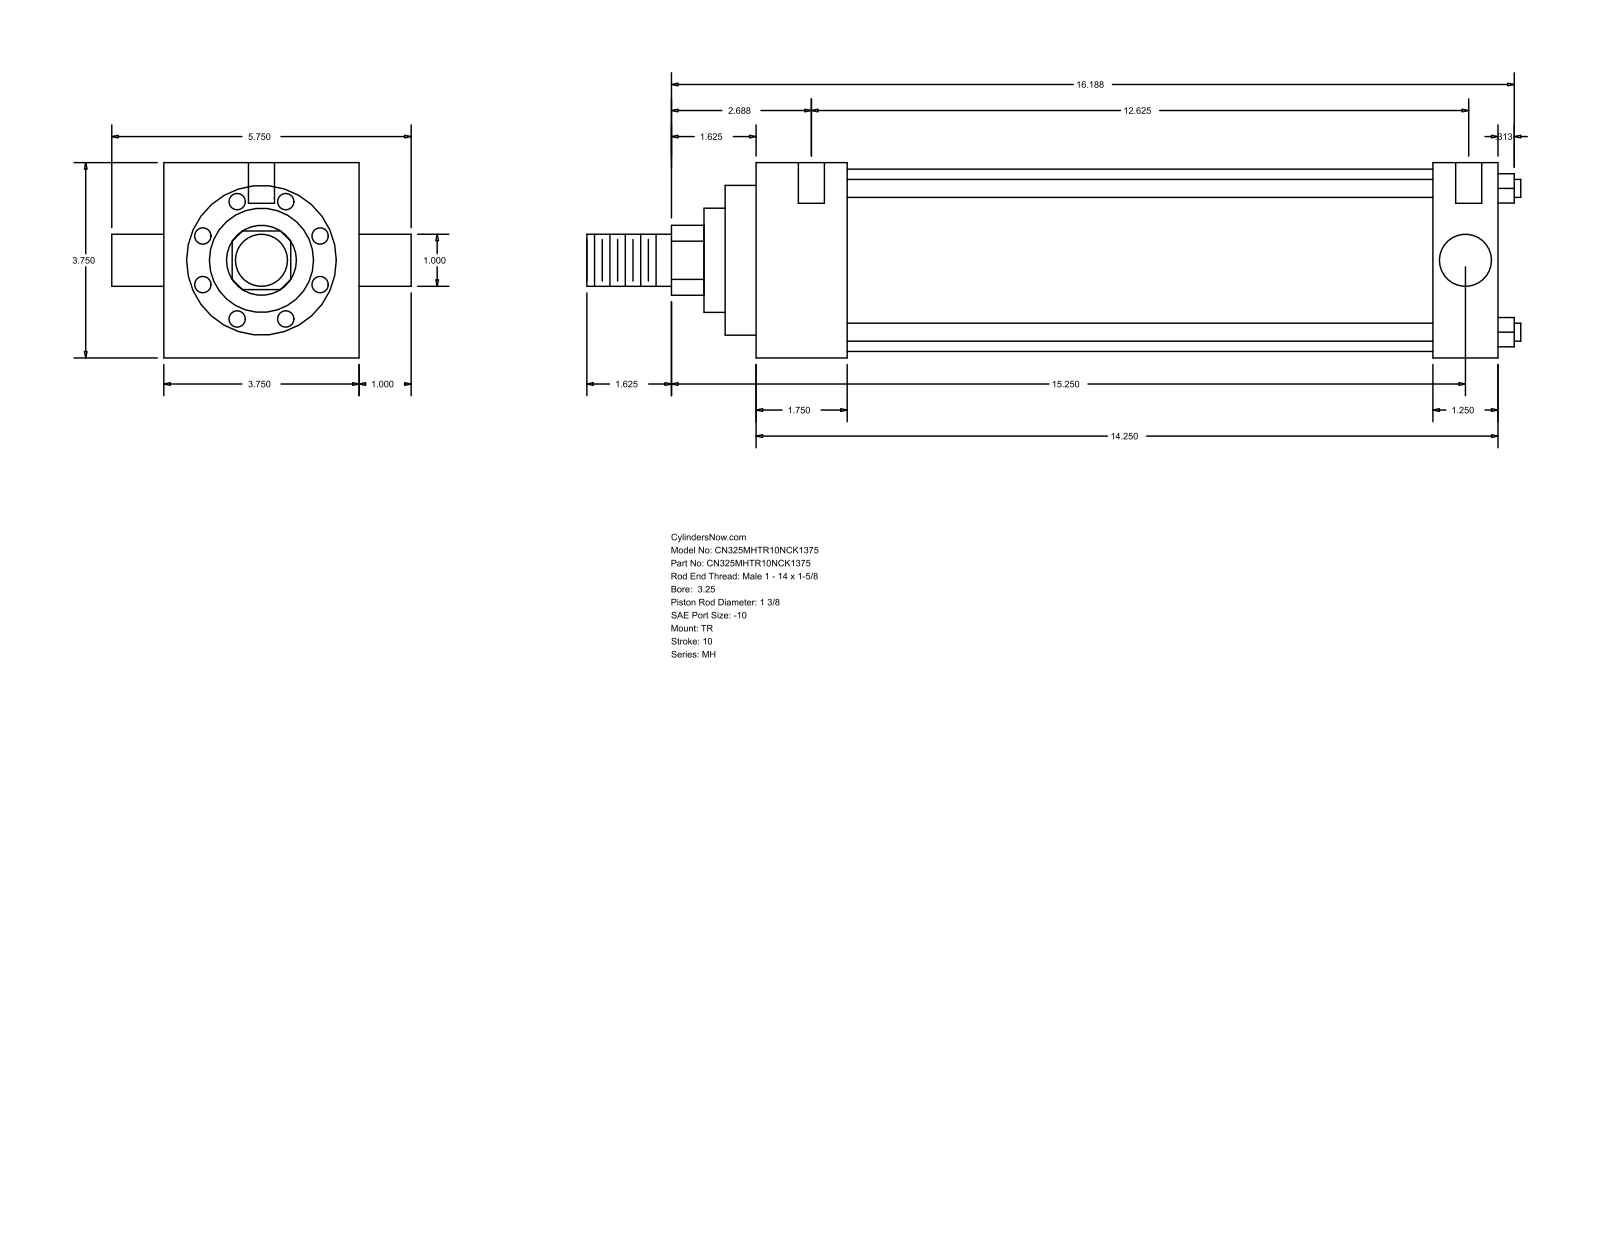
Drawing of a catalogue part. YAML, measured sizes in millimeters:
part_name: "MH_TR__0325_1.375"
step_written_by: "GSSL Pune (CONFIG_CONTROL_DESIGN)"
units: millimeters
bodies: {solids: 0, faces: 86, planar: 61, cylindrical: 25, other: 0}
overall_size: [455.61, 146.05, 95.25]
round_holes:
  - {diameter: 5.56, count: 3}
  - {diameter: 12.7, count: 2}
round_bosses_or_shafts:
  - {diameter: 8.76, count: 4}
  - {diameter: 25.4, count: 2}
  - {diameter: 88.9, count: 1}
  - {diameter: 73.03, count: 1}
  - {diameter: 50.8, count: 1}
  - {diameter: 34.92, count: 1}
partial_cylinders:
  - {radius: 17.06, count: 1}
face_to_face_distances: [95.24, 361.96, 44.45, 330.21, 285.76, 317.51, 31.75, 15.08, 59.53, 345.29]
hole_center_spacings: [1.59, 4.76, 320.68, 322.27, 325.44, 327.03]
